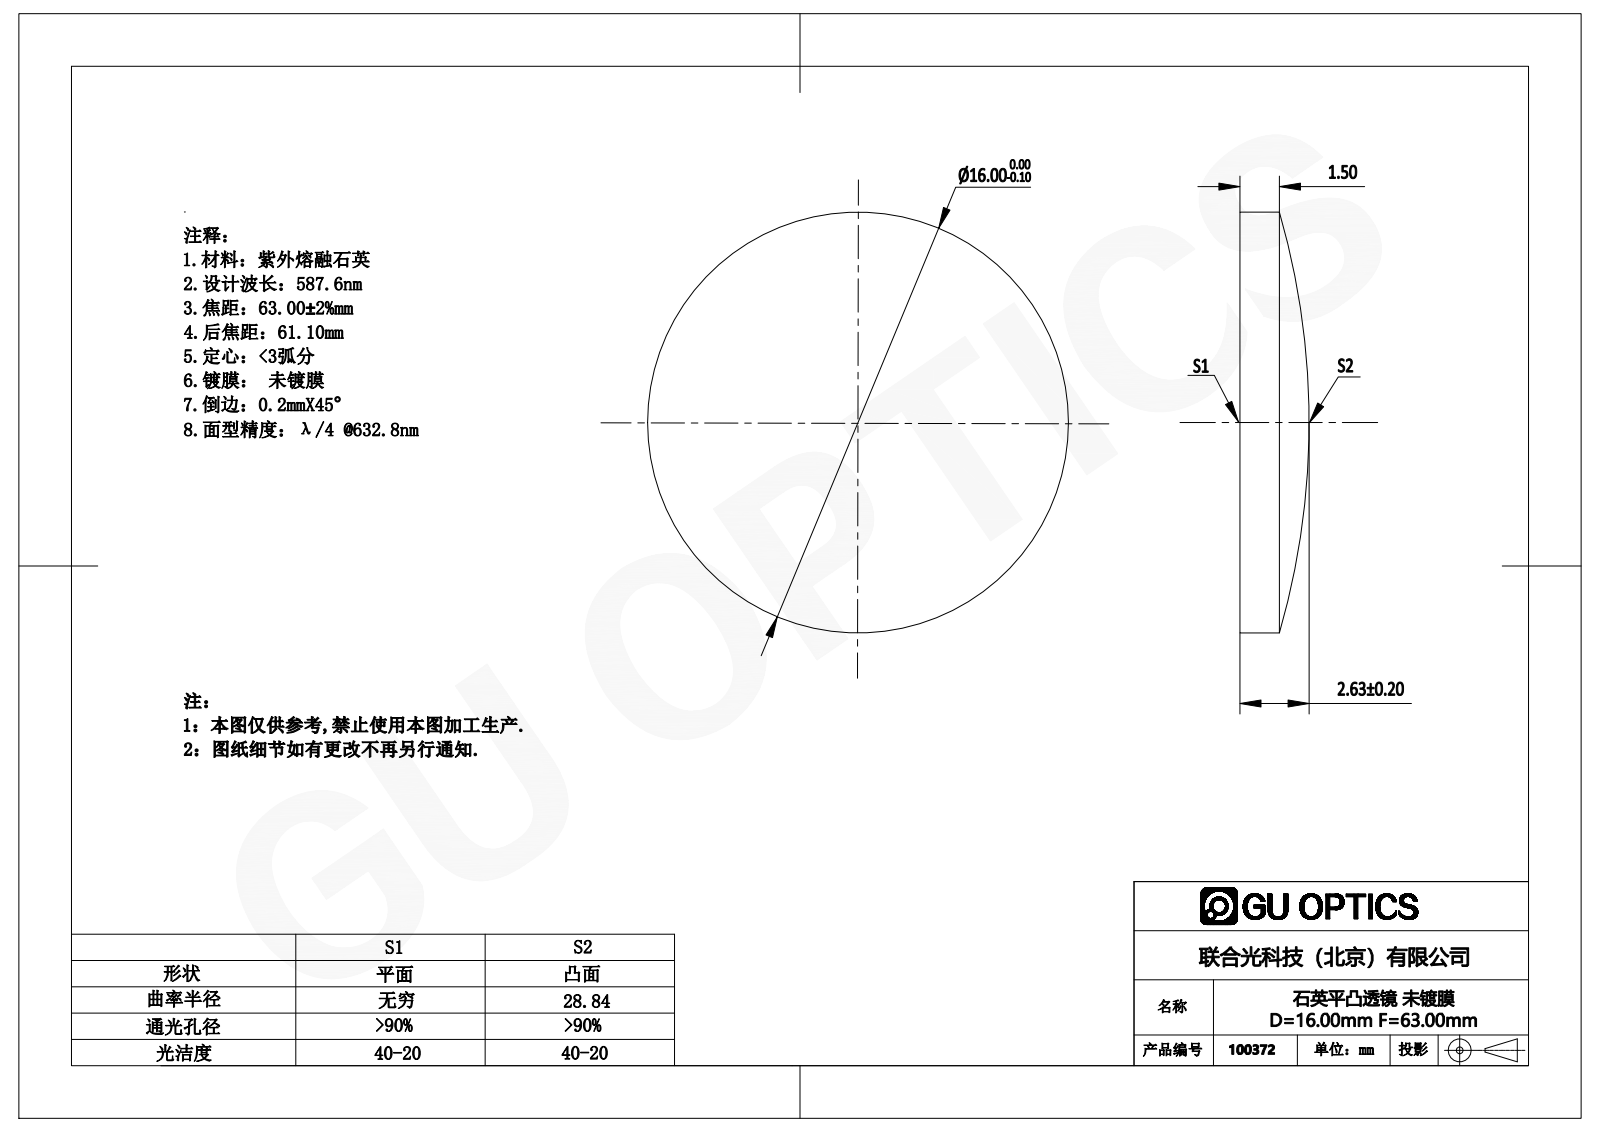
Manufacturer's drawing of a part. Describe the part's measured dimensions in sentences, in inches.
The part is named "100372". Its 3-D file was written by "SolidWorks 2016 (AUTOMOTIVE_DESIGN)". It is 1 solid with 5 faces: 1 planar, 2 cylindrical and 2 other. Overall it measures 0.63 by 0.63 by 0.104 inches. Its volume is 0.025 cubic inches and its surface area 0.747 square inches. Round bosses or shafts: 1 of diameter 0.63.
